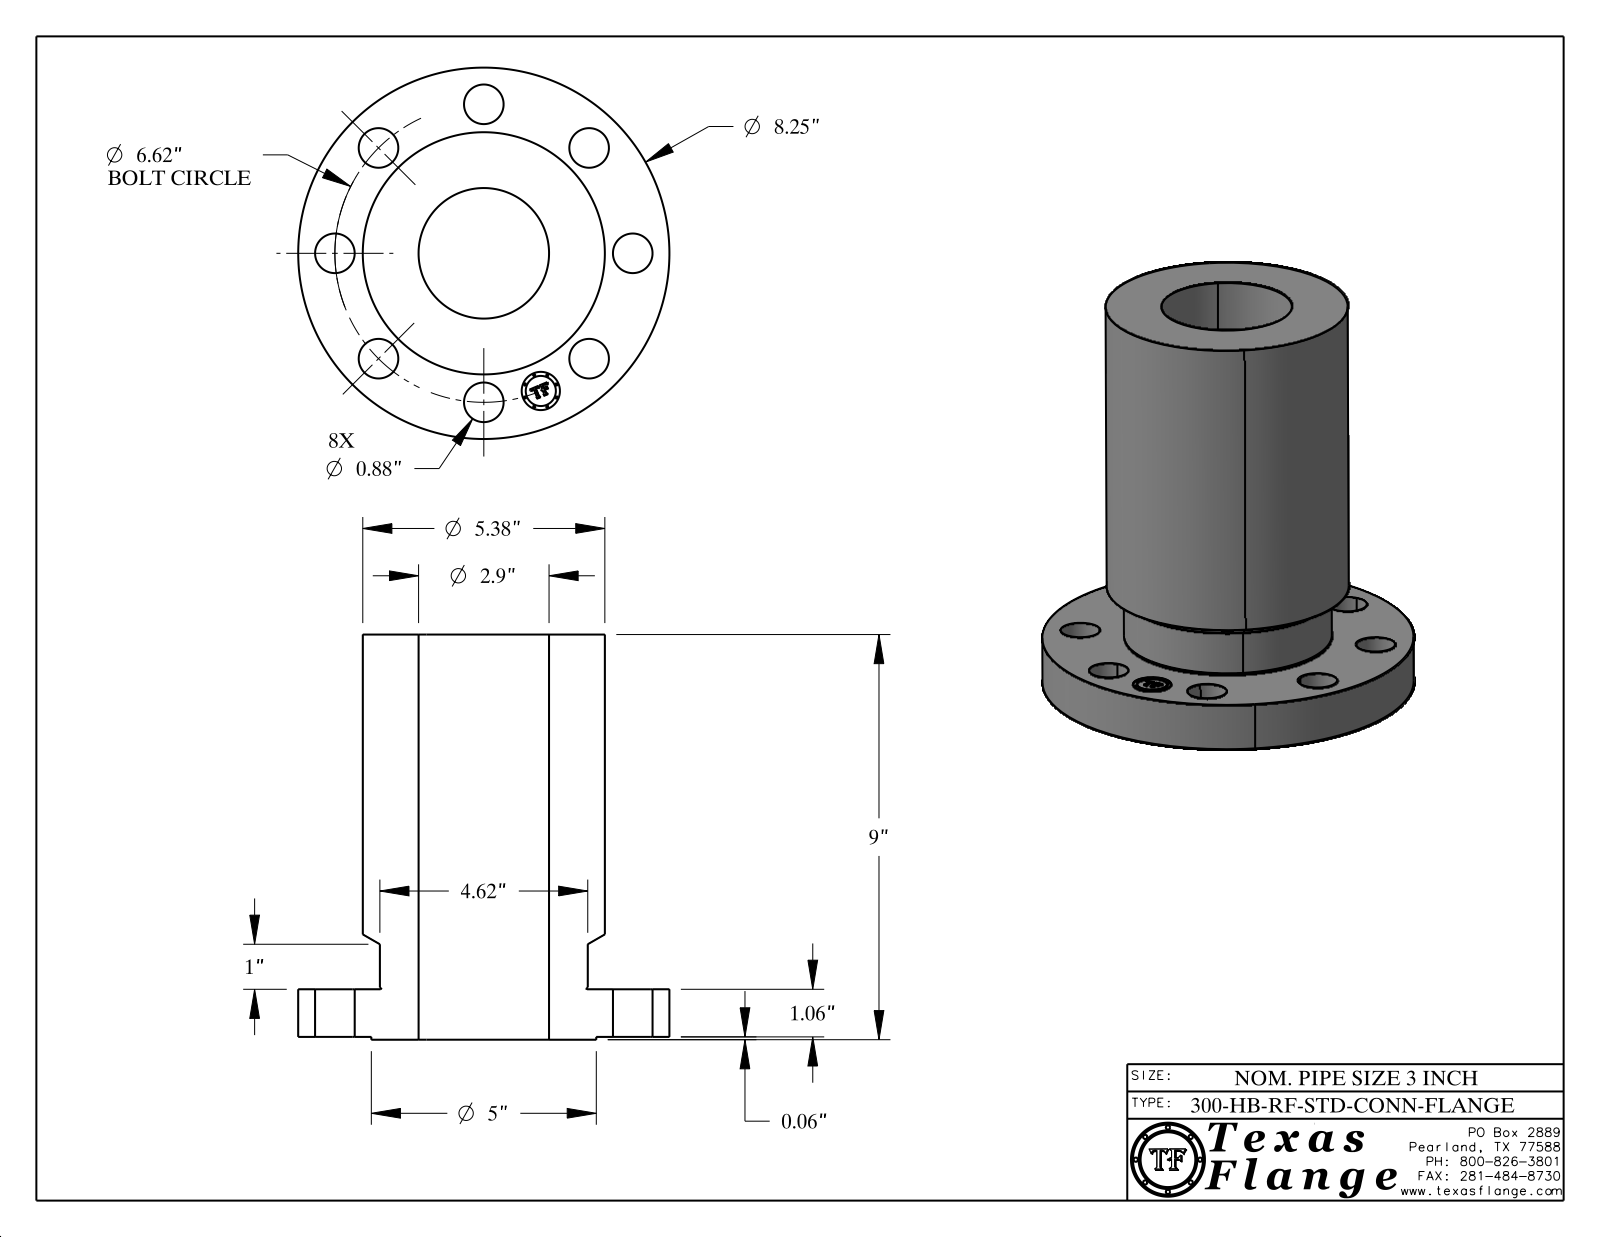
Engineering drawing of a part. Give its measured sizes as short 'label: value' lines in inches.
name: 3-300-HB-RF-STD-CONN-FLANGE
written by: CATIA V5 STEP AP214 (AUTOMOTIVE_DESIGN)
unit: in
bodies: 1 solid, 421 faces (369 planar, 46 cylindrical, 6 other)
size: 9 × 8.25 × 8.25
volume: 165.6 in³; area: 358.3 in²
holes: 8× ⌀0.88, 1× ⌀0.85, 1× ⌀2.9
bosses: 8× ⌀0.051, 1× ⌀8.25, 1× ⌀5.38, 1× ⌀5, 1× ⌀4.62, 1× ⌀0.67
face distances: 1.057, 8.937, 7.88, 0.063, 1.12, 9, 1.115, 1.052, 7.885, 0.016
hole spacings: 3.31, 2.533, 6.116, 4.681, 4.681, 1.291, 3.678, 6.493
